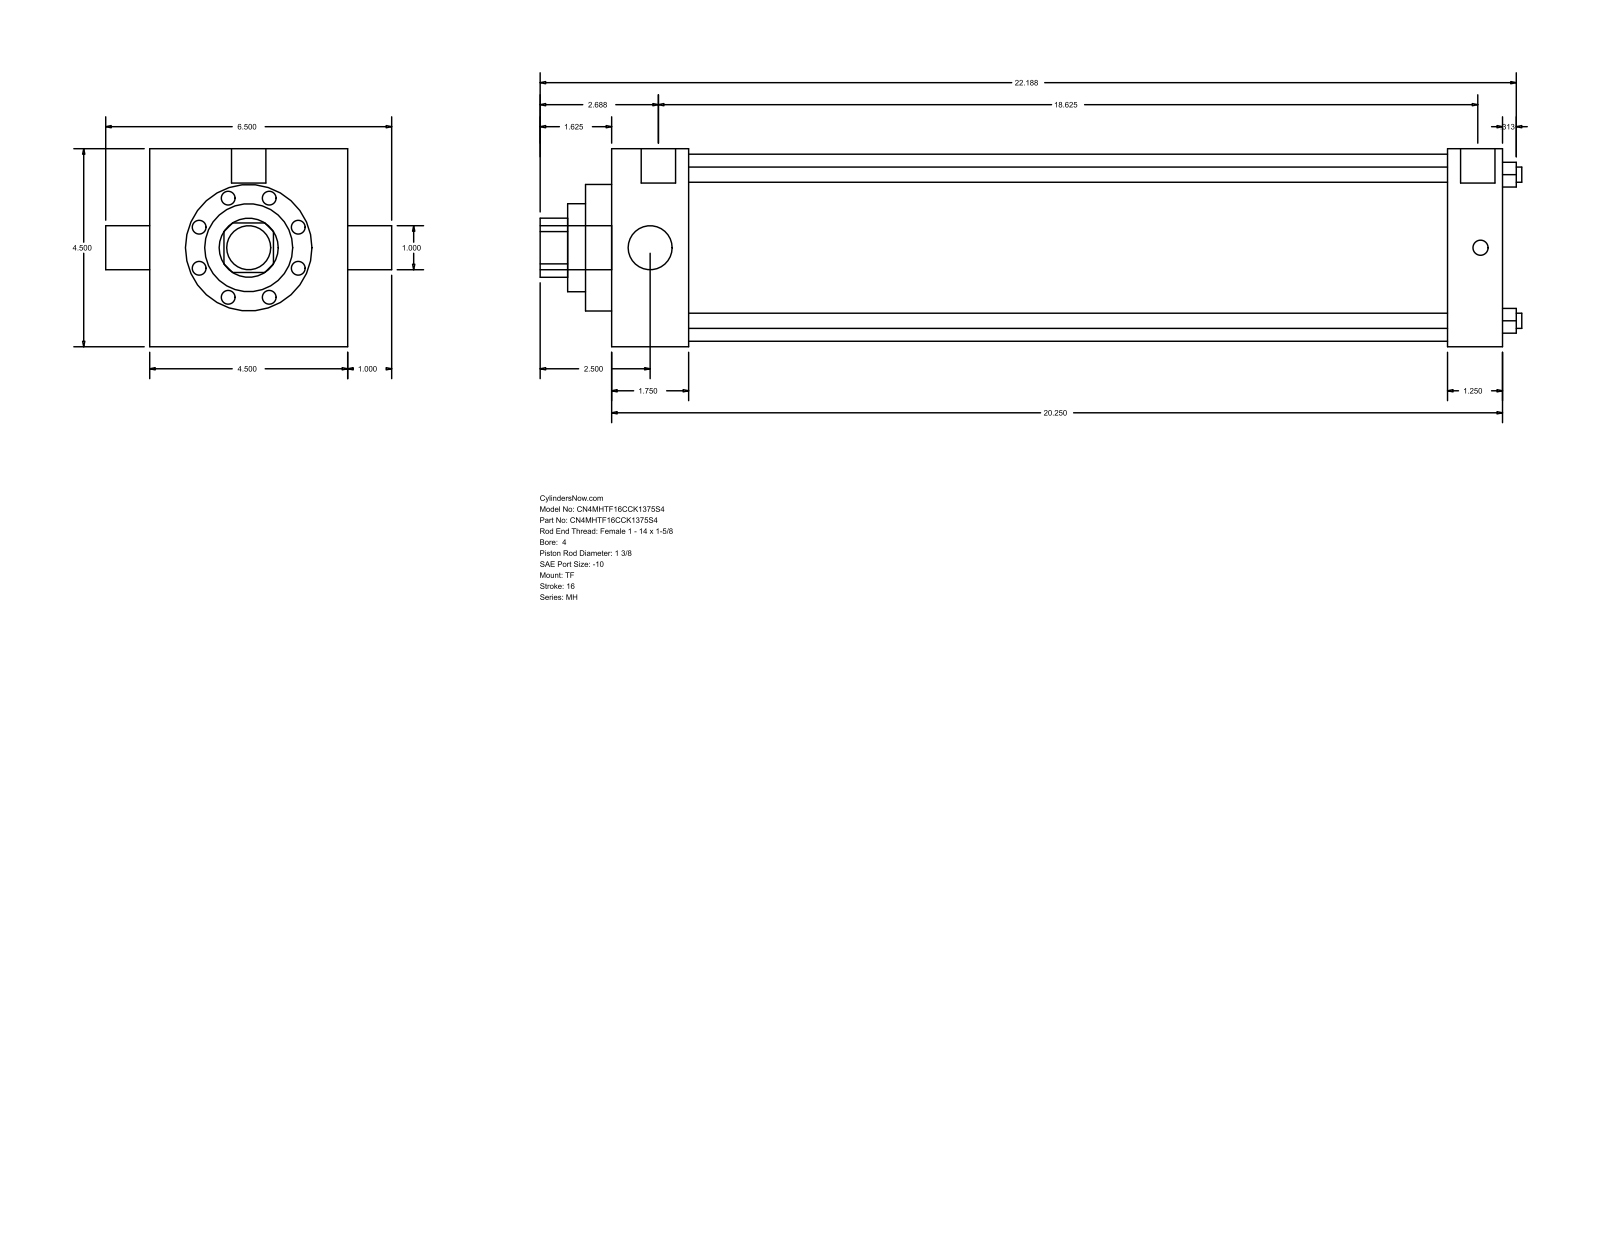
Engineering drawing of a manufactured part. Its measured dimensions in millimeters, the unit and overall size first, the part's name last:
Units: millimetres
Overall size (bounding box): 566.74 × 165.1 × 114.3
Round holes (diameter × count): ⌀8.76 ×4, ⌀25.4 ×1, ⌀34.92 ×1, ⌀50.8 ×1, ⌀73.03 ×1, ⌀107.95 ×1
Round bosses / shafts (diameter × count): ⌀8.73 ×3, ⌀19.84 ×2, ⌀25.4 ×1
Partial cylindrical surfaces — rounded edges, fillets, slot ends (radius × count): R17.06 ×1
Main face-to-face distances: 114.3, 514.35, 44.45, 469.9, 482.61, 438.16, 31.74, 15.08, 59.53, 497.69
Hole centre spacings: 59.62, 84.32, 119.25
Bodies: 0 solids, 86 faces (61 planar, 25 cylindrical, 0 other)
Part name (STEP PRODUCT): MH_TF__0400_1.375
STEP written by: GSSL Pune (CONFIG_CONTROL_DESIGN)
